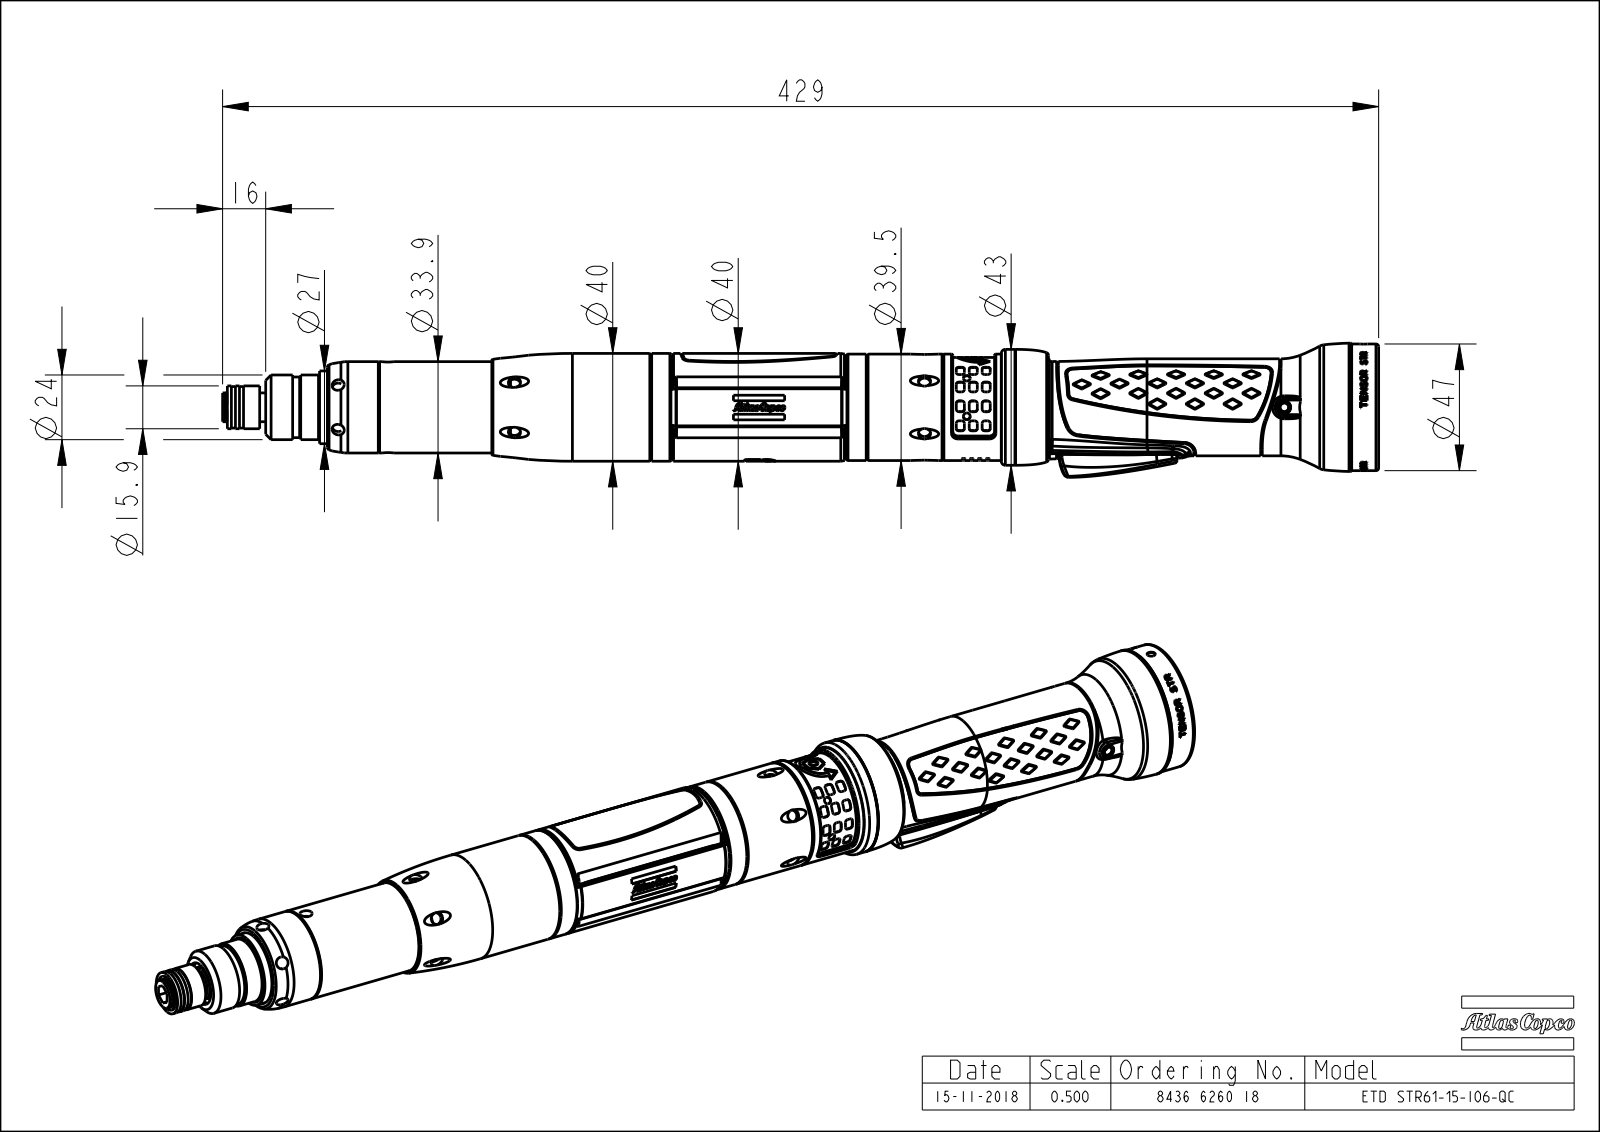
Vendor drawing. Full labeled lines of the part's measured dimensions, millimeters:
Part name (STEP PRODUCT): PRT0010
STEP written by: CREO PARAMETRIC BY PTC INC, 2018100 (CONFIG_CONTROL_DESIGN)
Units: millimetres
Bodies: 2 solids, 5299 faces (2121 planar, 934 cylindrical, 2244 other)
Overall size (bounding box): 428.39 × 49.81 × 47.62
Volume: 391 306 mm³ · Surface area: 117 938 mm²
Round holes (diameter × count): ⌀1 ×12, ⌀4.5 ×10, ⌀1.6 ×2, ⌀0.38 ×1, ⌀3 ×1, ⌀3.25 ×1, ⌀4.6 ×1, ⌀5 ×1, ⌀12 ×1, ⌀13 ×1, ⌀14 ×1, ⌀27.2 ×1
Round bosses / shafts (diameter × count): ⌀3.2 ×2, ⌀47 ×1, ⌀45.41 ×1, ⌀40 ×1, ⌀39.8 ×1, ⌀39.6 ×1, ⌀39.5 ×1, ⌀36.95 ×1
Partial cylindrical surfaces — rounded edges, fillets, slot ends (radius × count): R0.2 ×70, R0.3 ×48, R0.5 ×42, R2 ×28, R1 ×12, R3 ×12, R0.1 ×5, R1.5 ×5
Main face-to-face distances: 9.8, 208.33, 198.53, 138.9, 129.1, 69.43, 123.6, 113.8, 15.3, 84.73
Hole centre spacings: 3, 6, 9, 66.95, 152.23, 219.18, 4.99, 5.07
